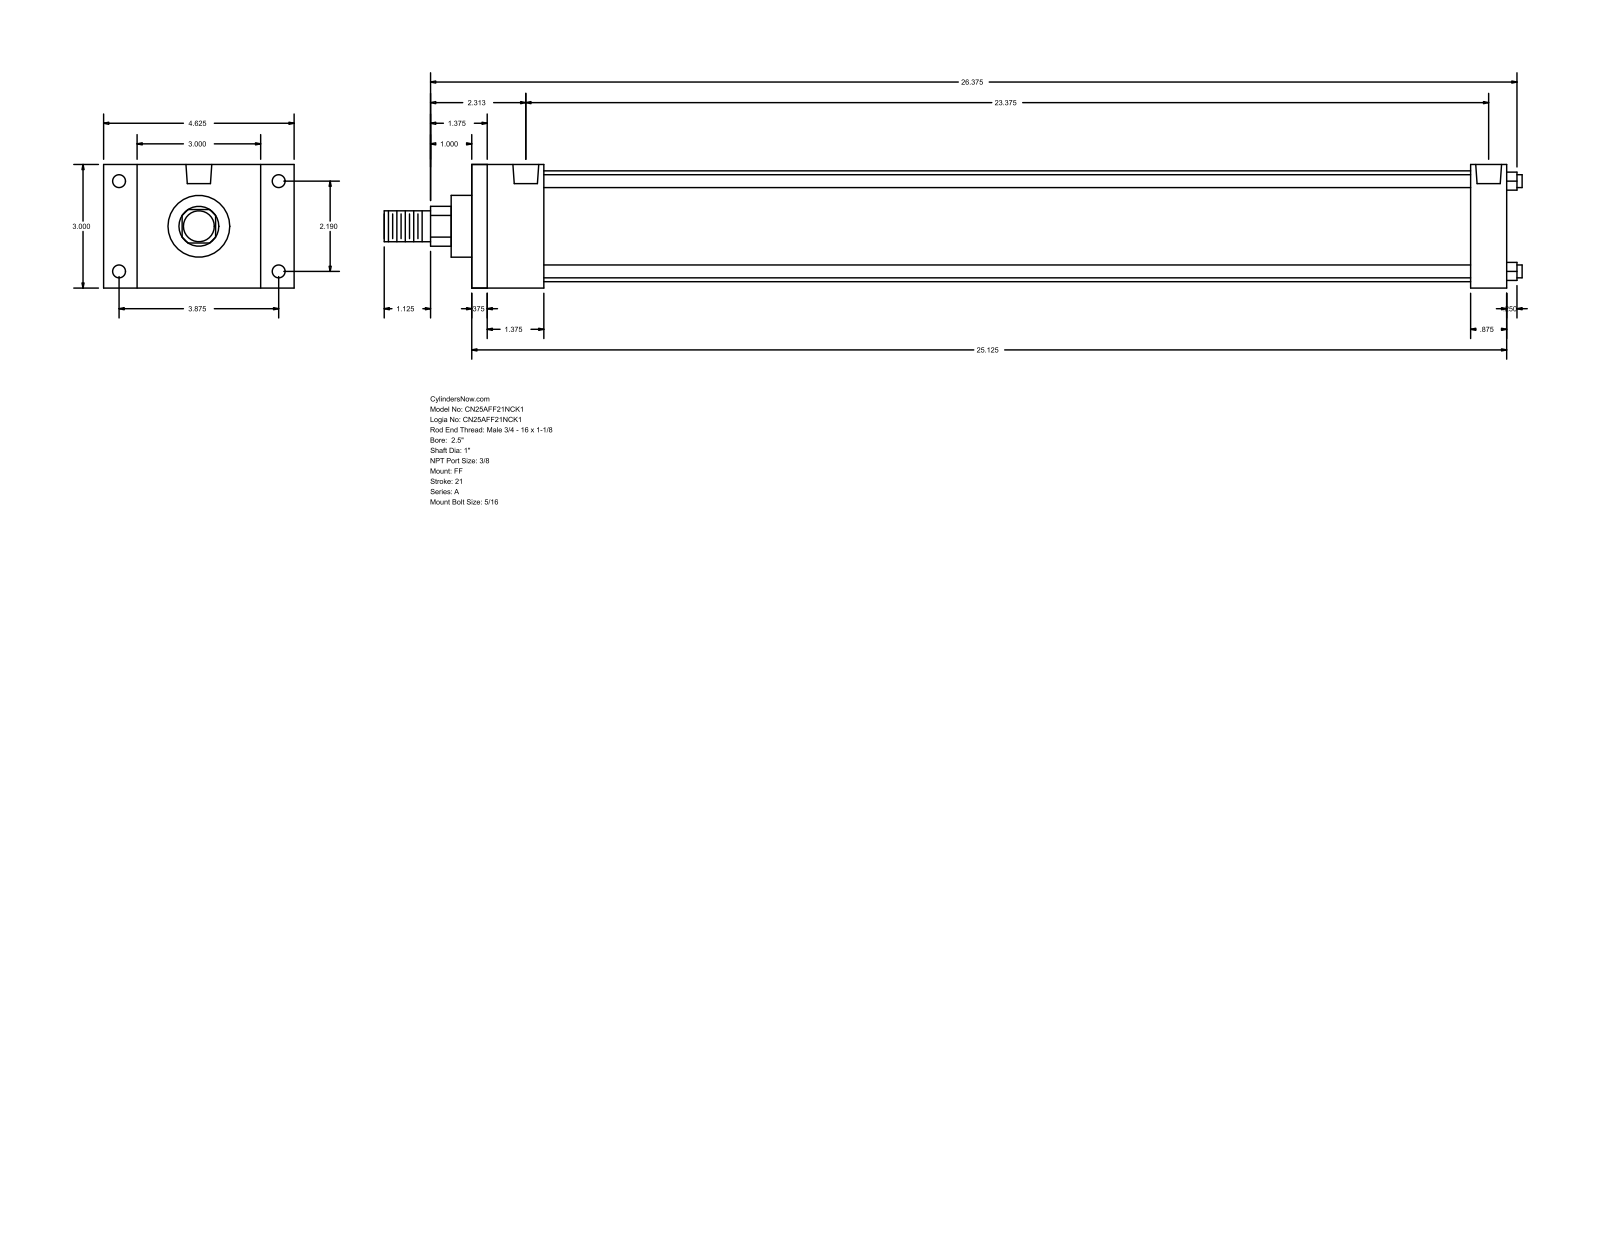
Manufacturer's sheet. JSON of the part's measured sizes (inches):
{"part_name": "A_FF__0250_1", "step_written_by": "GSSL Pune (CONFIG_CONTROL_DESIGN)", "units": "inches", "bodies": {"solids": 0, "faces": 92, "planar": 64, "cylindrical": 28, "other": 0}, "overall_size": [27.625, 4.625, 3], "round_holes": [[0.219, 4], [0.313, 4], [0.627, 2]], "round_bosses_or_shafts": [[0.313, 4], [2.69, 1], [1.5, 1], [1, 1], [0.75, 1]], "partial_cylinders_radius": [[0.484, 1]], "face_to_face_distances": [3, 25.125, 0.375, 24.75, 1.75, 24.25, 1.375, 23.875, 22.5, 23.375], "hole_center_spacings": [0.094, 2.19, 3.875, 4.451, 23.469, 23.562, 23.375]}
